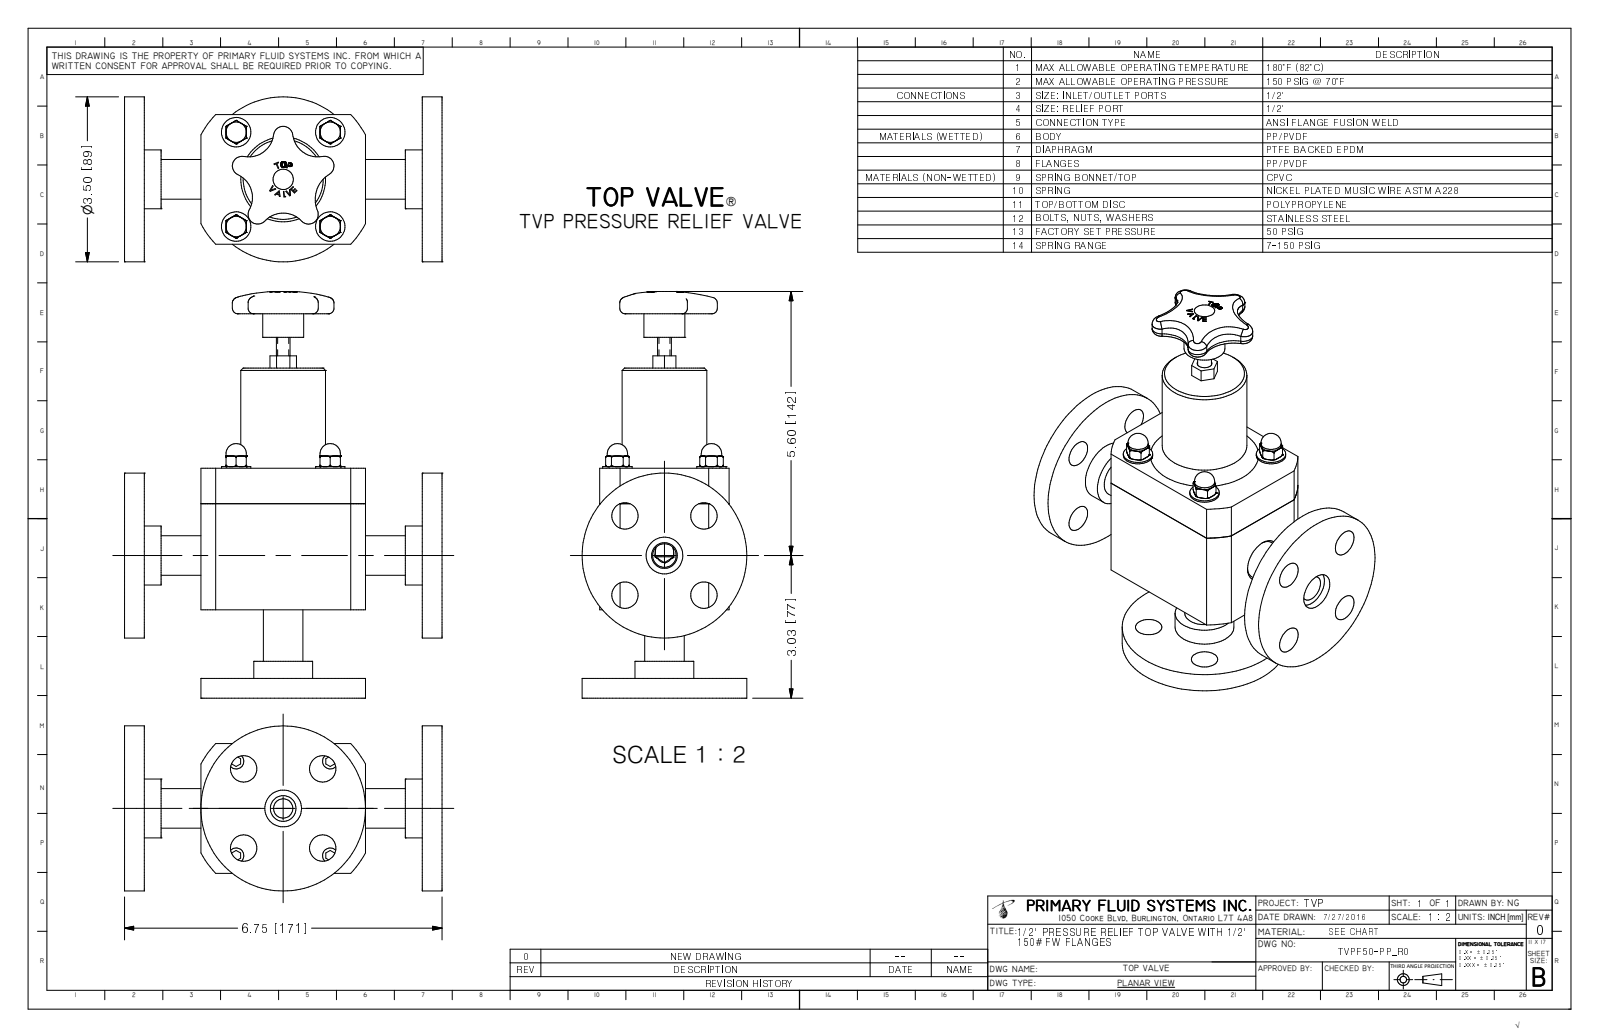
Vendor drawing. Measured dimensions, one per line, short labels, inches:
name: TVPF50-PP_R0
written by: Autodesk Inventor 2009 (AUTOMOTIVE_DESIGN)
unit: in
bodies: 1 solid, 339 faces (135 planar, 68 cylindrical, 136 other)
size: 8.625 × 6.75 × 3.5
volume: 47.41 in³; area: 173.3 in²
holes: 8× ⌀0.56, 4× ⌀0.175, 2× ⌀0.546, 2× ⌀0.78, 1× ⌀2.4
bosses: 4× ⌀0.625, 4× ⌀0.433, 2× ⌀3.5, 2× ⌀1.25, 2× ⌀0.84, 1× ⌀2.375, 1× ⌀1.8, 1× ⌀0.87
rounds: 5× R0.085, 5× R0.205, 4× R0.536, 4× R0.656, 1× R0.625, 1× R0.745, 1× R1.988
face distances: 0.42, 6.33, 5.125, 1.625, 1.205, 4.705, 2.75, 1.875, 6.75, 1.455
hole spacings: 1.188, 1.68, 1.847, 0.227, 1.414, 2, 2.375, 2.602
